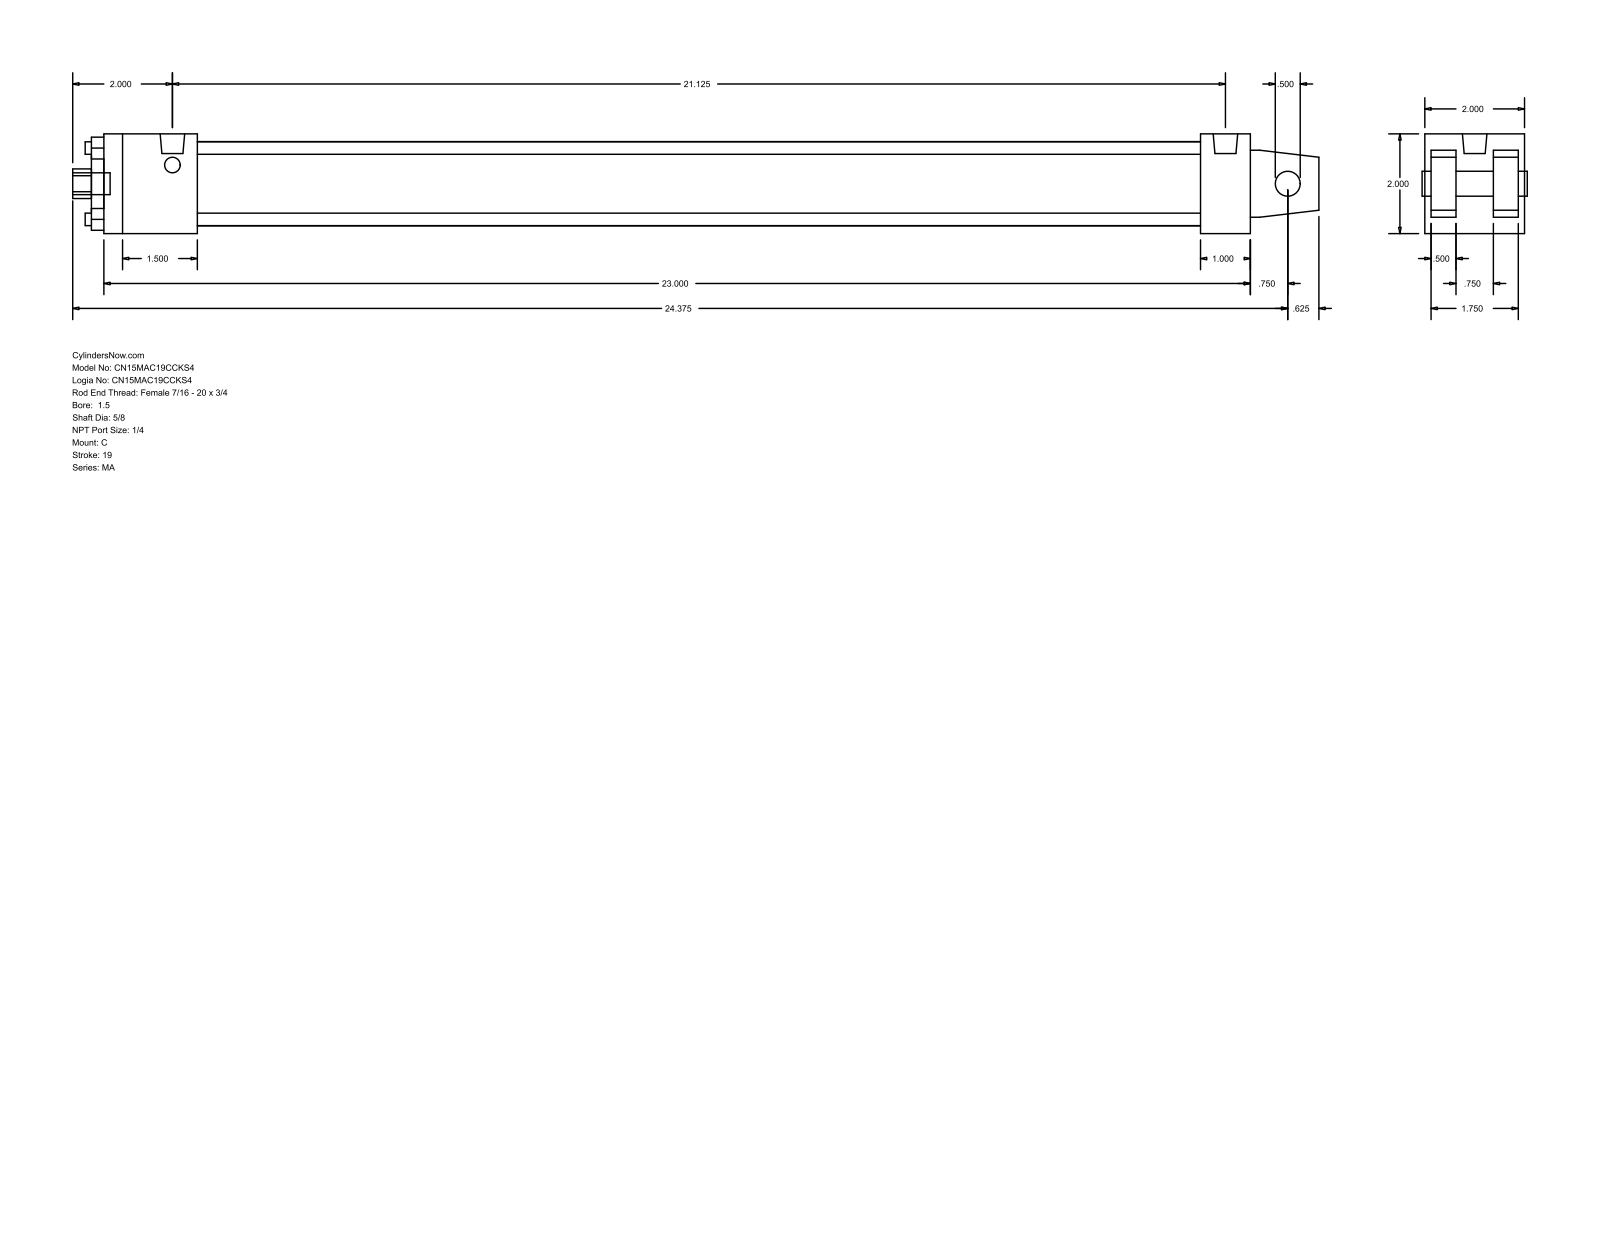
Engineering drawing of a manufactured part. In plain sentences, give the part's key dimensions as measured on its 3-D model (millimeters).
The part is named "MA_C__0150_0.625". Its 3-D file was written by "GSSL Pune (CONFIG_CONTROL_DESIGN)". It is 0 solids with 103 faces: 76 planar, 27 cylindrical and 0 other. Overall it measures 635 by 50.8 by 50.8 millimeters. Round holes: 4 of diameter 6.35, 1 of diameter 12.7, 1 of diameter 15.88, 1 of diameter 28.57, 1 of diameter 42.93. Round bosses or shafts: 4 of diameter 7.94, 2 of diameter 12.49, 1 of diameter 11.11. Partial cylindrical surfaces (rounded edges, fillets, slot ends): 1 of radius 7.54. The main face-to-face distances are 50.8, 12.7, 3.17, 15.87, 34.93, 47.63, 31.76, 584.2, 558.79, 25.41. The hole center spacings are 25.68, 36.32, 51.36.
